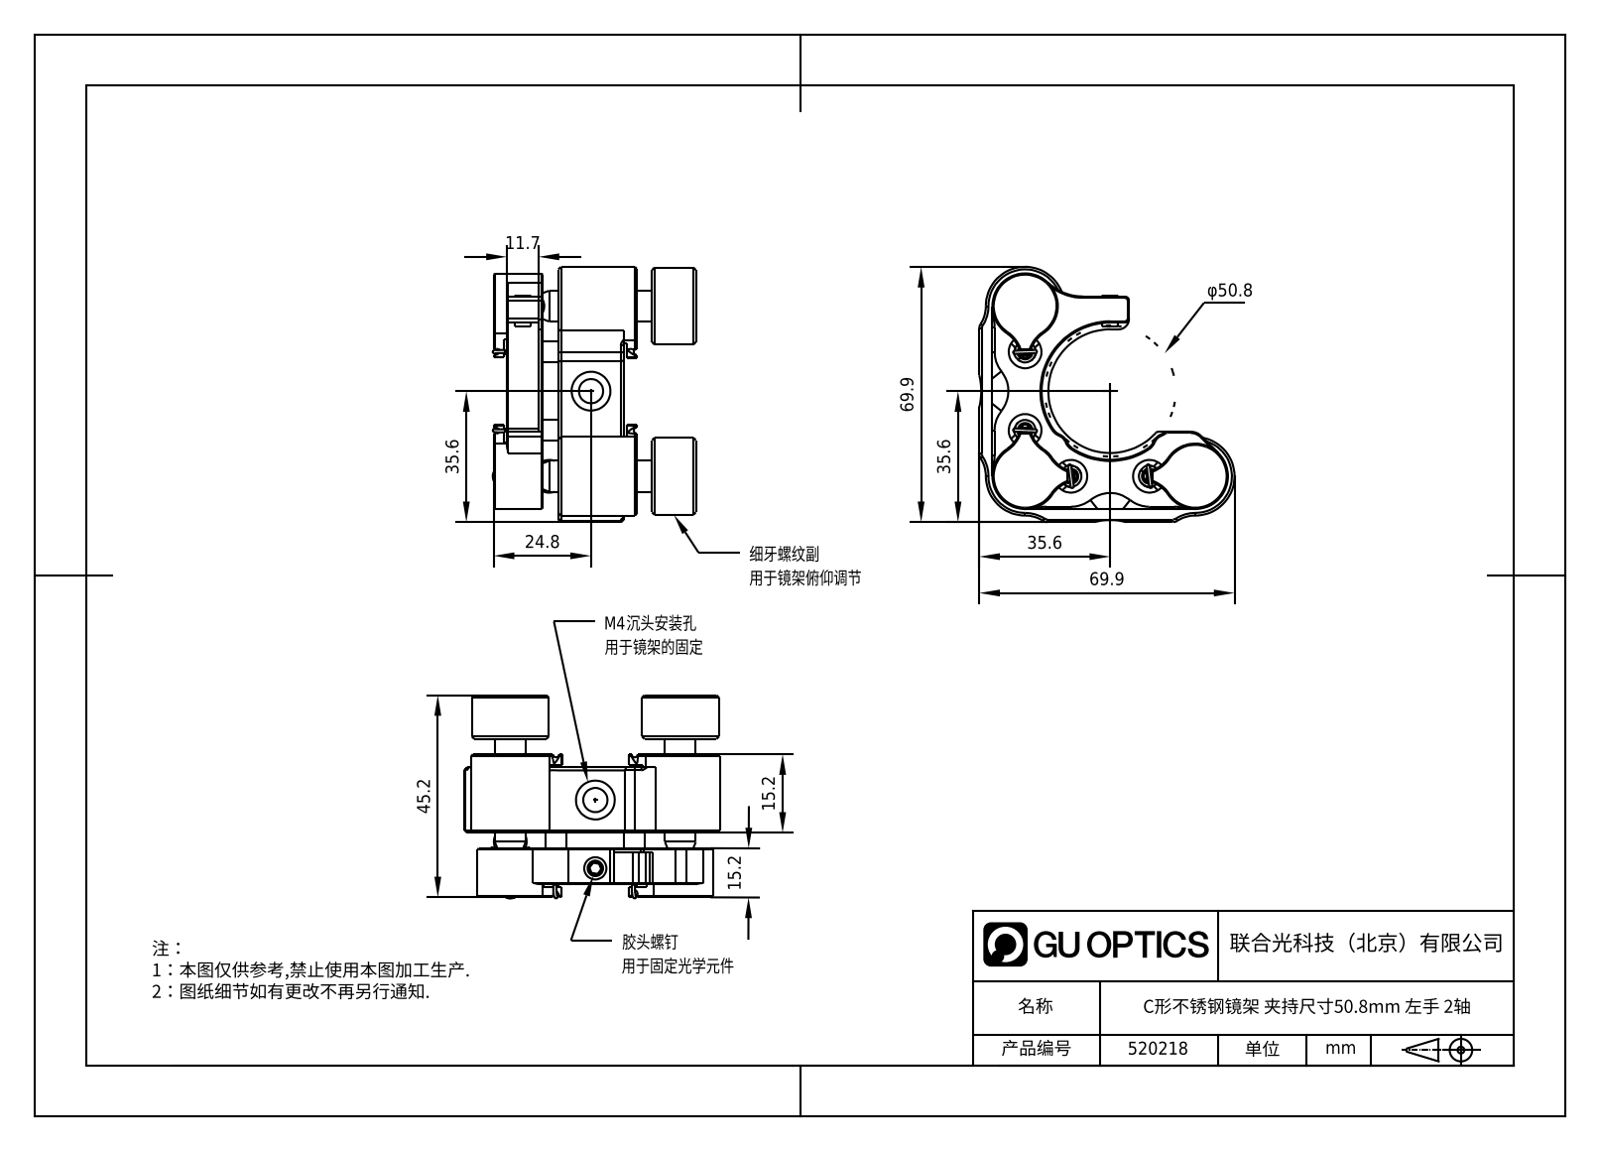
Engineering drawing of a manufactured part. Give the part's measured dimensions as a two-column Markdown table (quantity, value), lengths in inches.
| quantity | value |
| --- | --- |
| part name | 36.1，440c不锈钢滚珠_36.1.8_GZ-B6; DXVS，真空型M6x0.25六角调节器，零部件，Rev.A_3.2.11.2.1-DXVS-0625-26.6; 36.1，440c不锈钢滚珠_36.1.6_GZ-B4; DXG，平面螺纹旋钮_3.2.10.19-DXG-M0625-15-8.5S (+3 more) |
| STEP written by | SolidWorks 2021 (CONFIG_CONTROL_DESIGN) |
| units | inches |
| bodies | 21 solids, 724 faces (193 planar, 187 cylindrical, 344 other) |
| overall size | 2.75 × 2.75 × 1.781 |
| volume | 2.307 in³ |
| surface area | 34.92 in² |
| round holes (diameter × count) | 0.25 × 6, 0.185 × 4, 0.297 × 4, 0.071 × 2, 0.079 × 2, 0.13 × 2, 0.157 × 2, 0.157 × 2, 0.236 × 2, 0.276 × 2 |
| round bosses / shafts (diameter × count) | 0.157 × 8, 0.6 × 2, 0.591 × 2, 0.197 × 2, 0.118 × 2 |
| partial cylindrical surfaces (radius × count) | 0.255 × 19, 0.125 × 8, 0.118 × 5, 0.039 × 4, 0.157 × 4, 2.525 × 4, 0.024 × 3, 0.25 × 3 |
| main face-to-face distances | 0.5, 0.625, 0.1, 0.125, 0.6, 0.725, 1.225, 1.125, 1.325, 0.456 |
| hole center spacings | 0.197, 0.372, 0.374, 0.571, 1.357, 1.728, 1.768, 2.133 |
